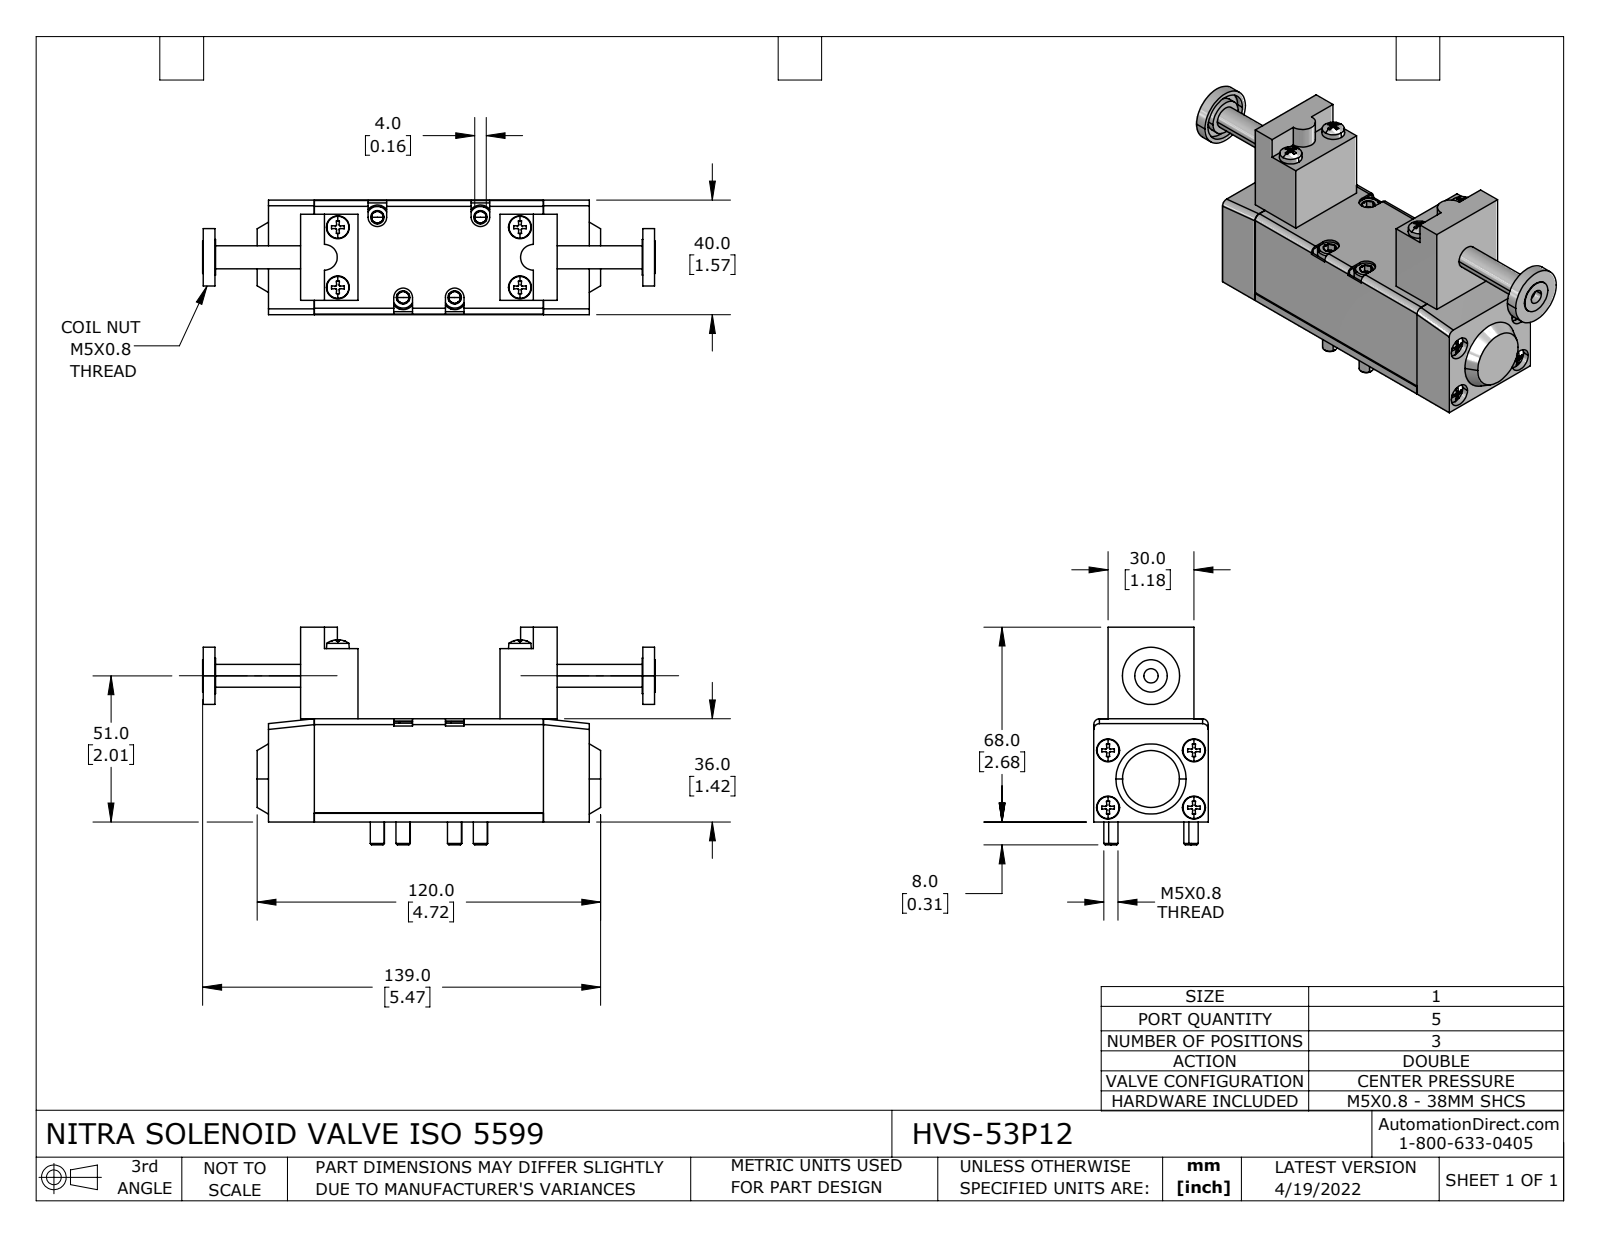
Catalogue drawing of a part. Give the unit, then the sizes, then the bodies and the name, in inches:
Units: inches
Overall size (bounding box): 6.22 × 2.992 × 1.575
Round holes (diameter × count): ⌀0.128 ×8, ⌀0.161 ×4, ⌀0.217 ×4, ⌀0.315 ×4, ⌀0.197 ×1, ⌀0.665 ×1
Round bosses / shafts (diameter × count): ⌀0.157 ×8, ⌀0.335 ×4, ⌀0.197 ×4, ⌀0.787 ×1, ⌀0.488 ×1, ⌀0.445 ×1, ⌀0.315 ×1
Partial cylindrical surfaces — rounded edges, fillets, slot ends (radius × count): R0.079 ×6, R0.128 ×4, R0.197 ×4, R0.177 ×2
Main face-to-face distances: 0.189, 1.417, 3.15, 1.567, 1.559, 3.339, 0.197, 1.378, 1.37, 0.787
Hole centre spacings: 0.561, 0.787, 0.827, 0.908, 1.107, 1.158, 1.181, 1.182
Volume: 12.18 in³ · Surface area: 84.18 in²
Bodies: 21 solids, 850 faces (434 planar, 156 cylindrical, 260 other)
Part name (STEP PRODUCT): HVS-53P12
STEP written by: SolidWorks 2021 (CONFIG_CONTROL_DESIGN)
